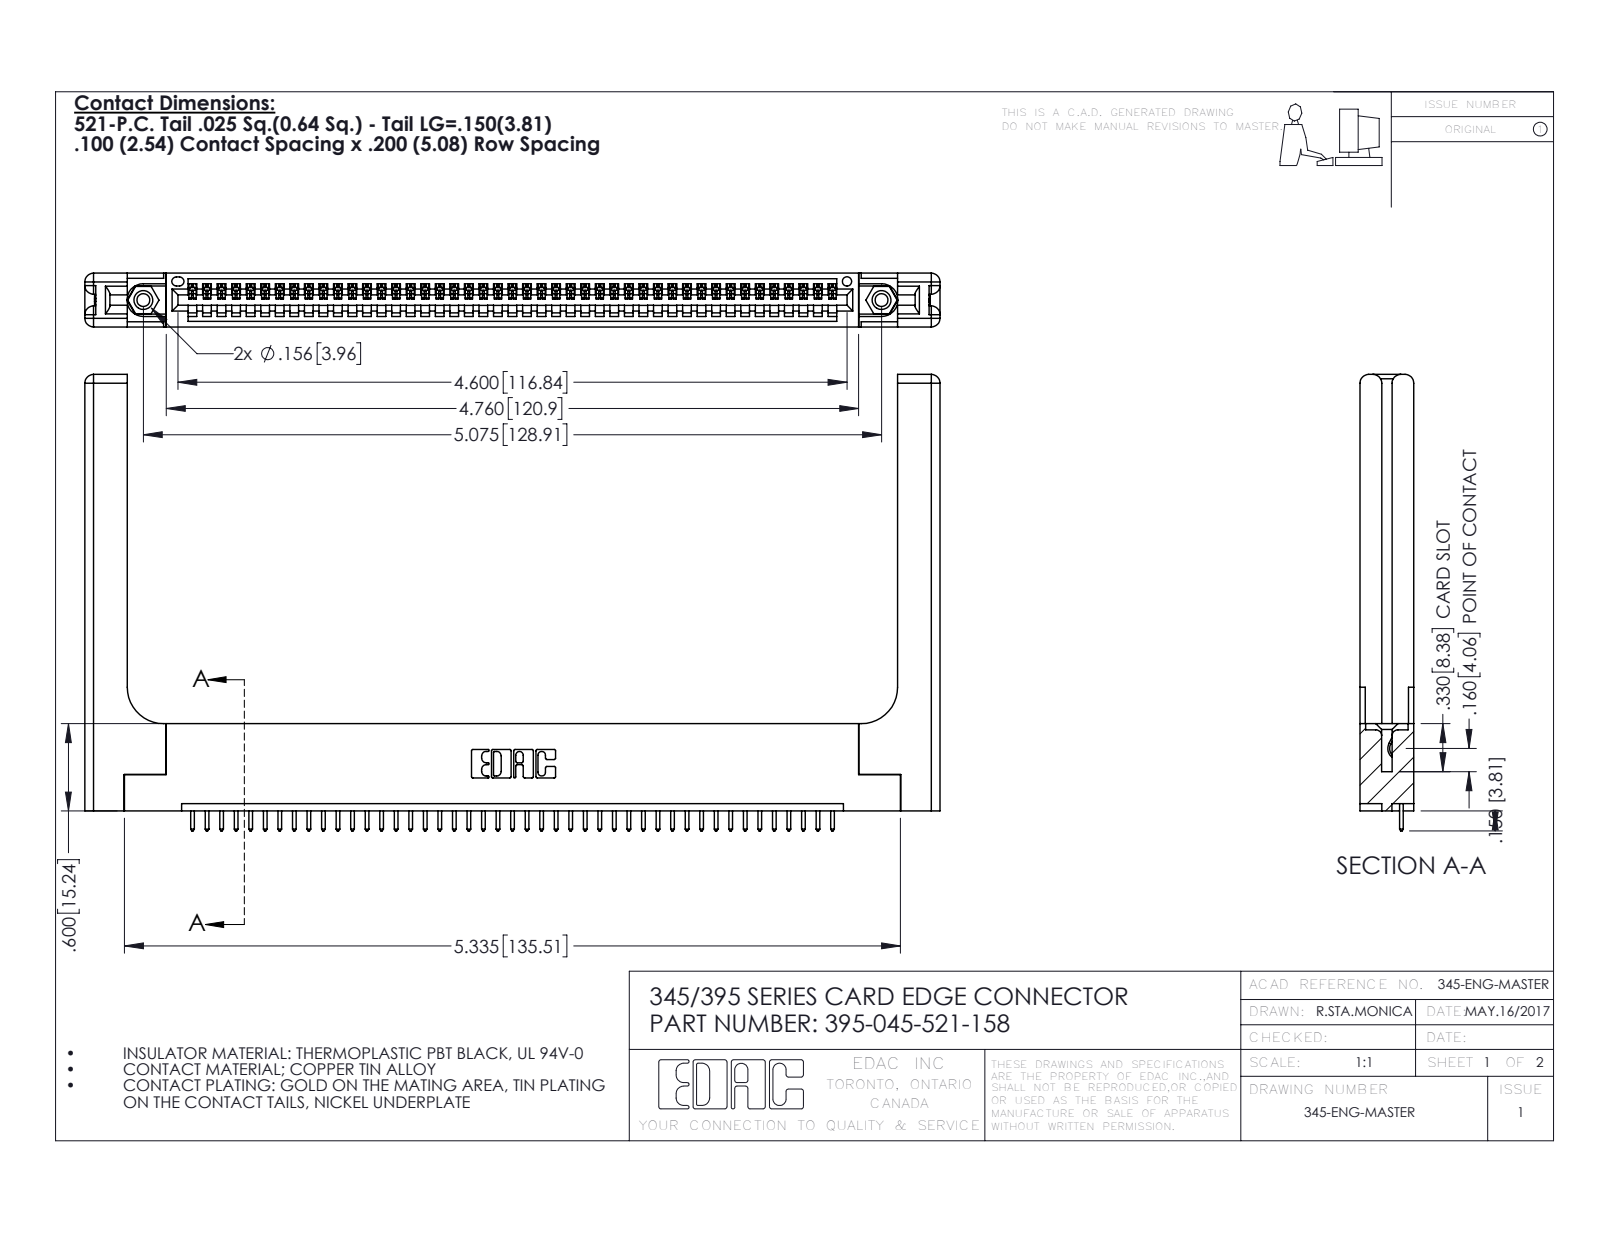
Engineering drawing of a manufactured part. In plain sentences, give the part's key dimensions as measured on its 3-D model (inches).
The part is named "395-045-521-158; 345-250-001_345-250-001-102; 345-220-058_345-220-058; 345-292-001_345-293-121 (+1 more)". Its 3-D file was written by "SolidWorks 2016 (CONFIG_CONTROL_DESIGN)". It is 50 solids with 2992 faces: 2028 planar, 904 cylindrical and 60 other. Overall it measures 5.879 by 3.137 by 0.37 inches. Its volume is 1.378 cubic inches and its surface area 36.51 square inches. Round holes: 2 of diameter 0.089, 2 of diameter 0.125, 2 of diameter 0.156, 1 of diameter 0.064. Round bosses or shafts: 2 of diameter 0.155. Partial cylindrical surfaces (rounded edges, fillets, slot ends): 90 of radius 0.006, 90 of radius 0.01, 22 of radius 0.01, 16 of radius 0.06, 6 of radius 0.007, 6 of radius 0.031, 3 of radius 0.026, 2 of radius 0.03. The main face-to-face distances are 0.37, 0.072, 0.298, 0.2, 0.098, 0.272, 0.025, 0.225, 0.148, 0.15. The hole center spacings are 0.27, 4.839, 5.075.
